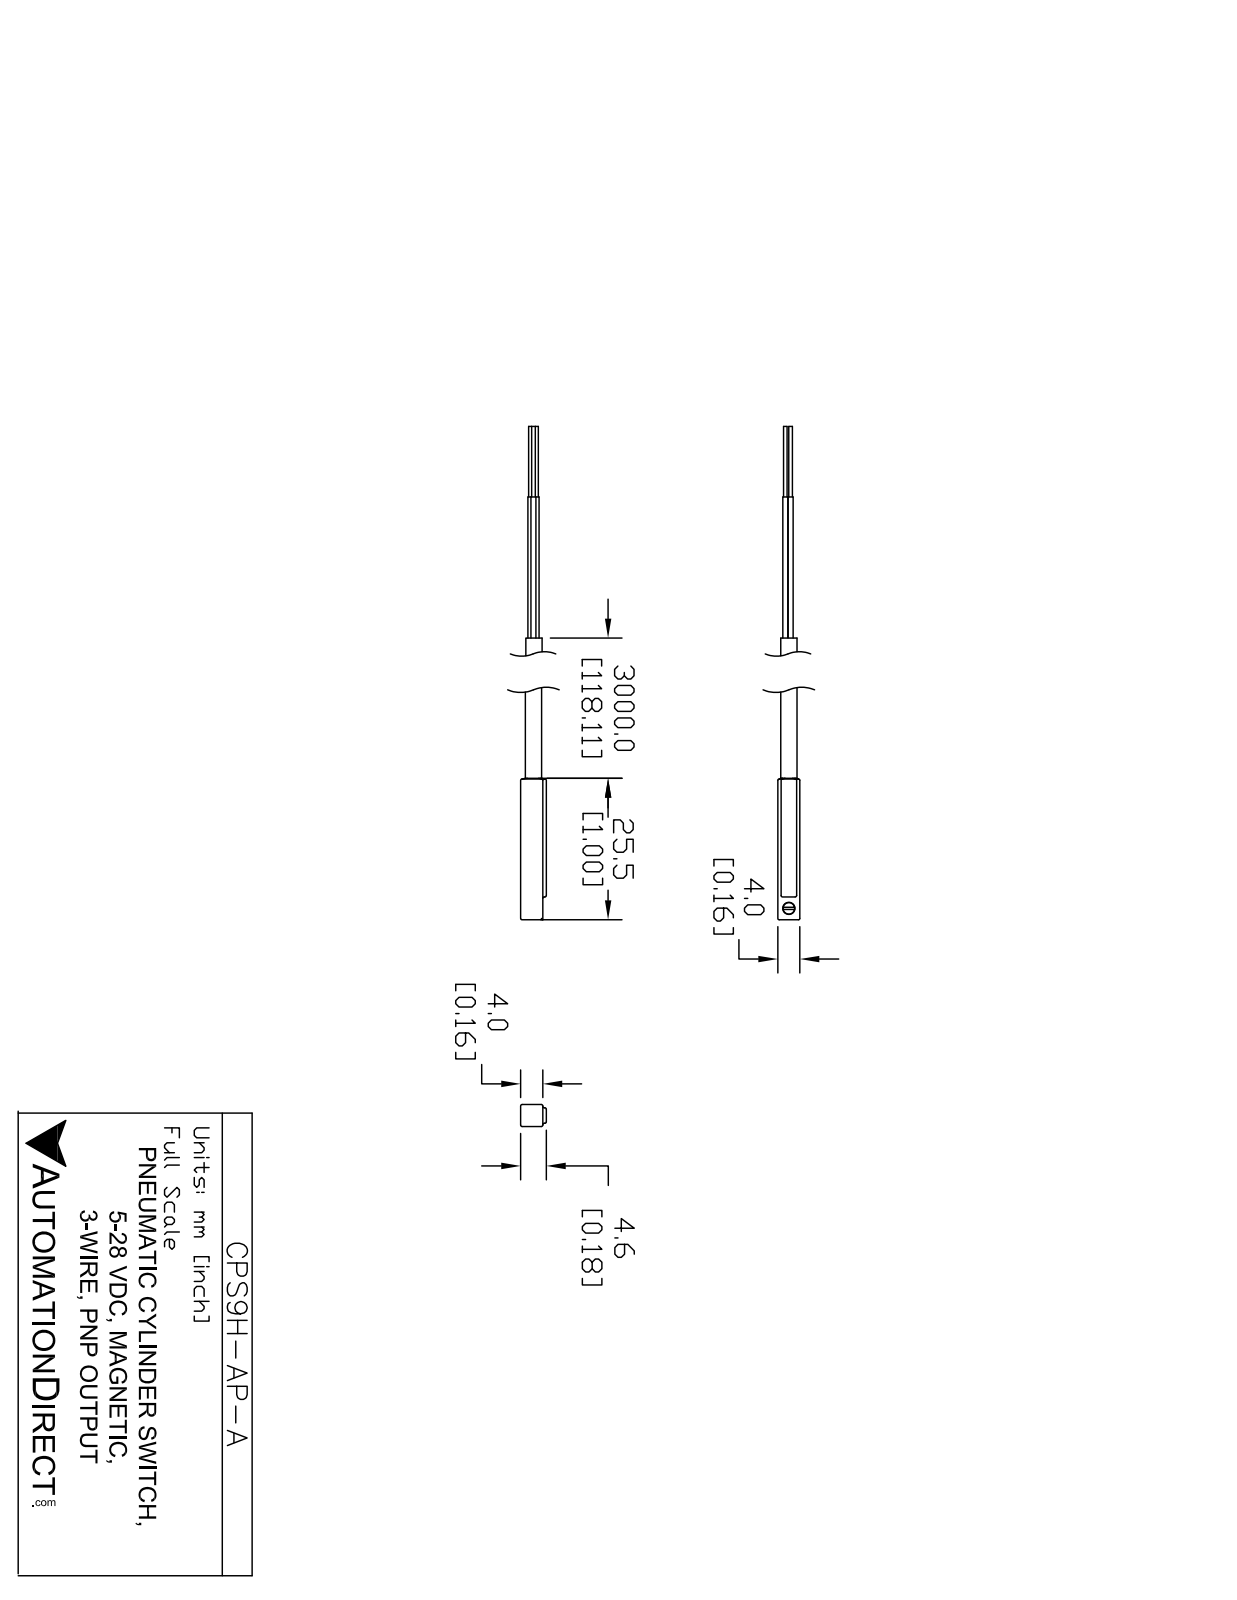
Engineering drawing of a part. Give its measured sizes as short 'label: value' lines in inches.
name: 9H72-000-031SW.igs2_1; 9H72-000-031SW.igs1_1; CPS9H-AP-A
written by: SolidWorks 2014 (AUTOMOTIVE_DESIGN)
unit: in
bodies: 2 solids, 97 faces (22 planar, 41 cylindrical, 34 other)
size: 6.498 × 0.182 × 0.156
volume: 0.072 in³; area: 2.663 in²
holes: 1× ⌀0.086
bosses: 3× ⌀0.035, 3× ⌀0.025, 1× ⌀0.115, 1× ⌀0.082
rounds: 22× R0.01
face distances: 0.156, 0.182, 0.157, 0.025, 0.023, 0.133, 4.998, 0.11, 0.015, 1.5
